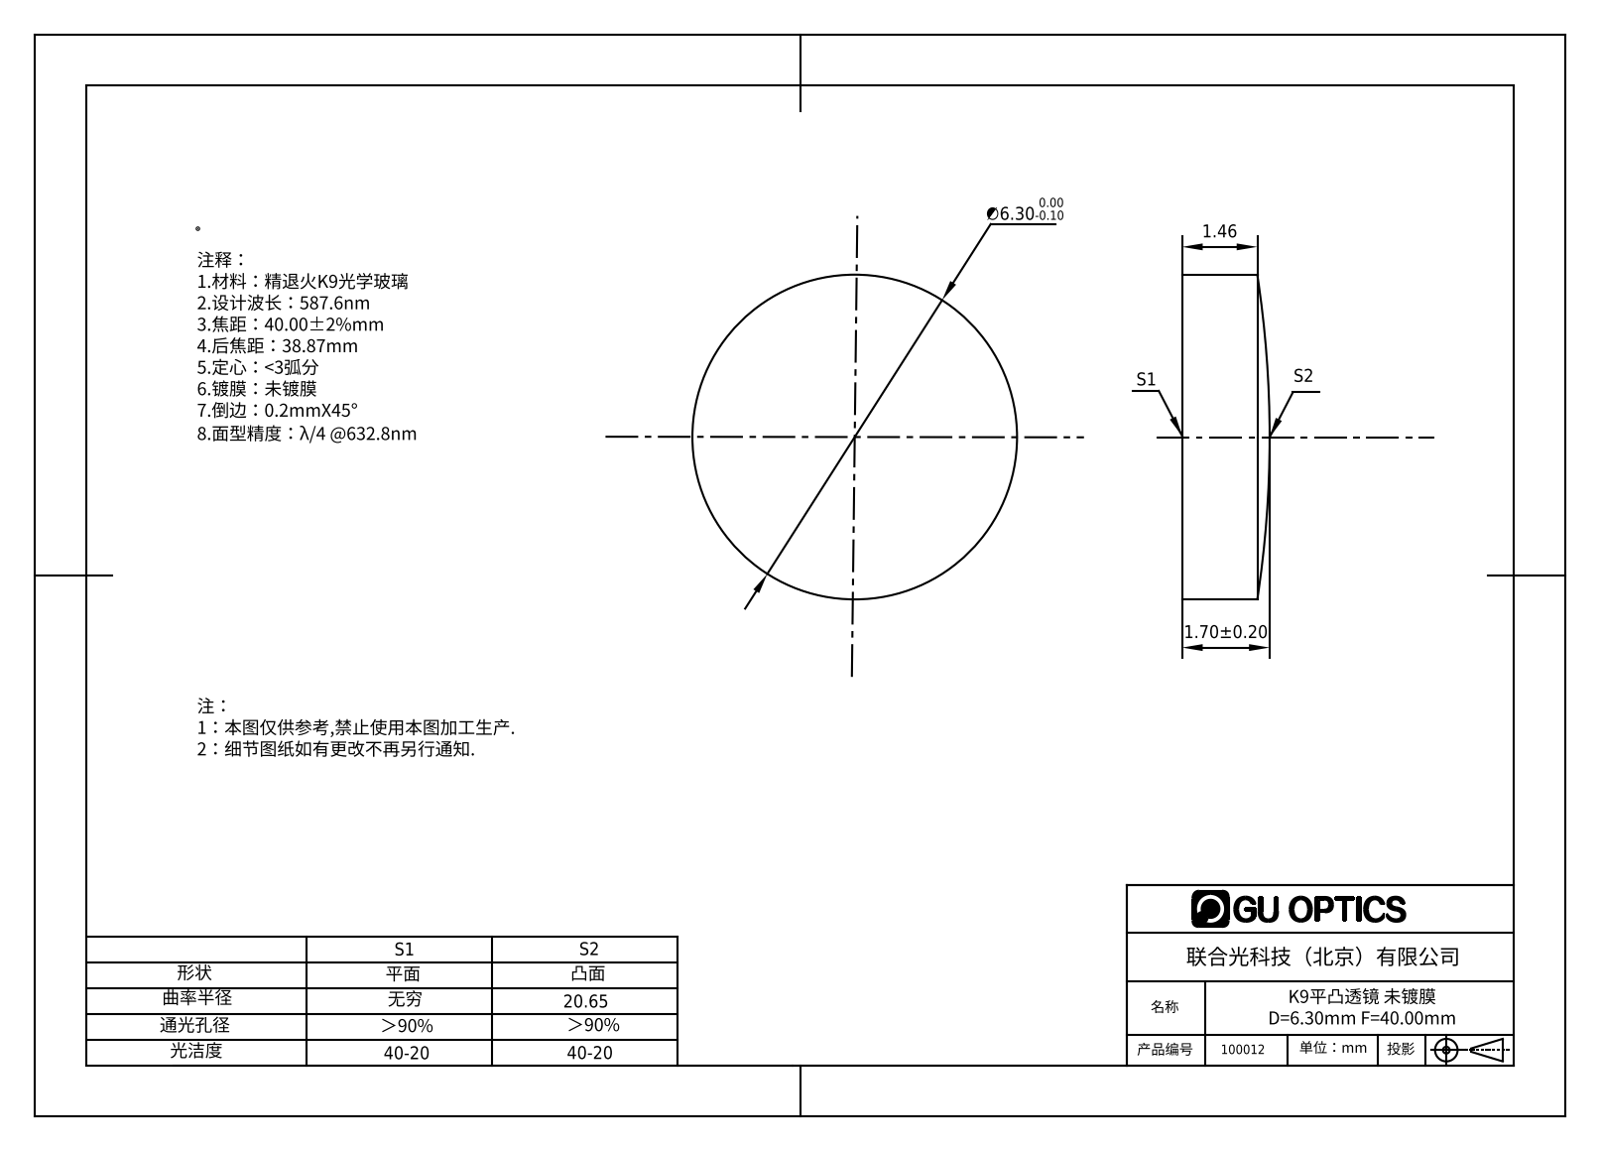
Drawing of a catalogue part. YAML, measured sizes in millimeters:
part_name: "100012"
step_written_by: "SolidWorks 2016 (AUTOMOTIVE_DESIGN)"
units: millimeters
bodies: {solids: 1, faces: 5, planar: 1, cylindrical: 2, other: 2}
overall_size: [6.3, 6.3, 1.7]
volume: 49
surface_area: 91
round_bosses_or_shafts:
  - {diameter: 6.3, count: 1}
